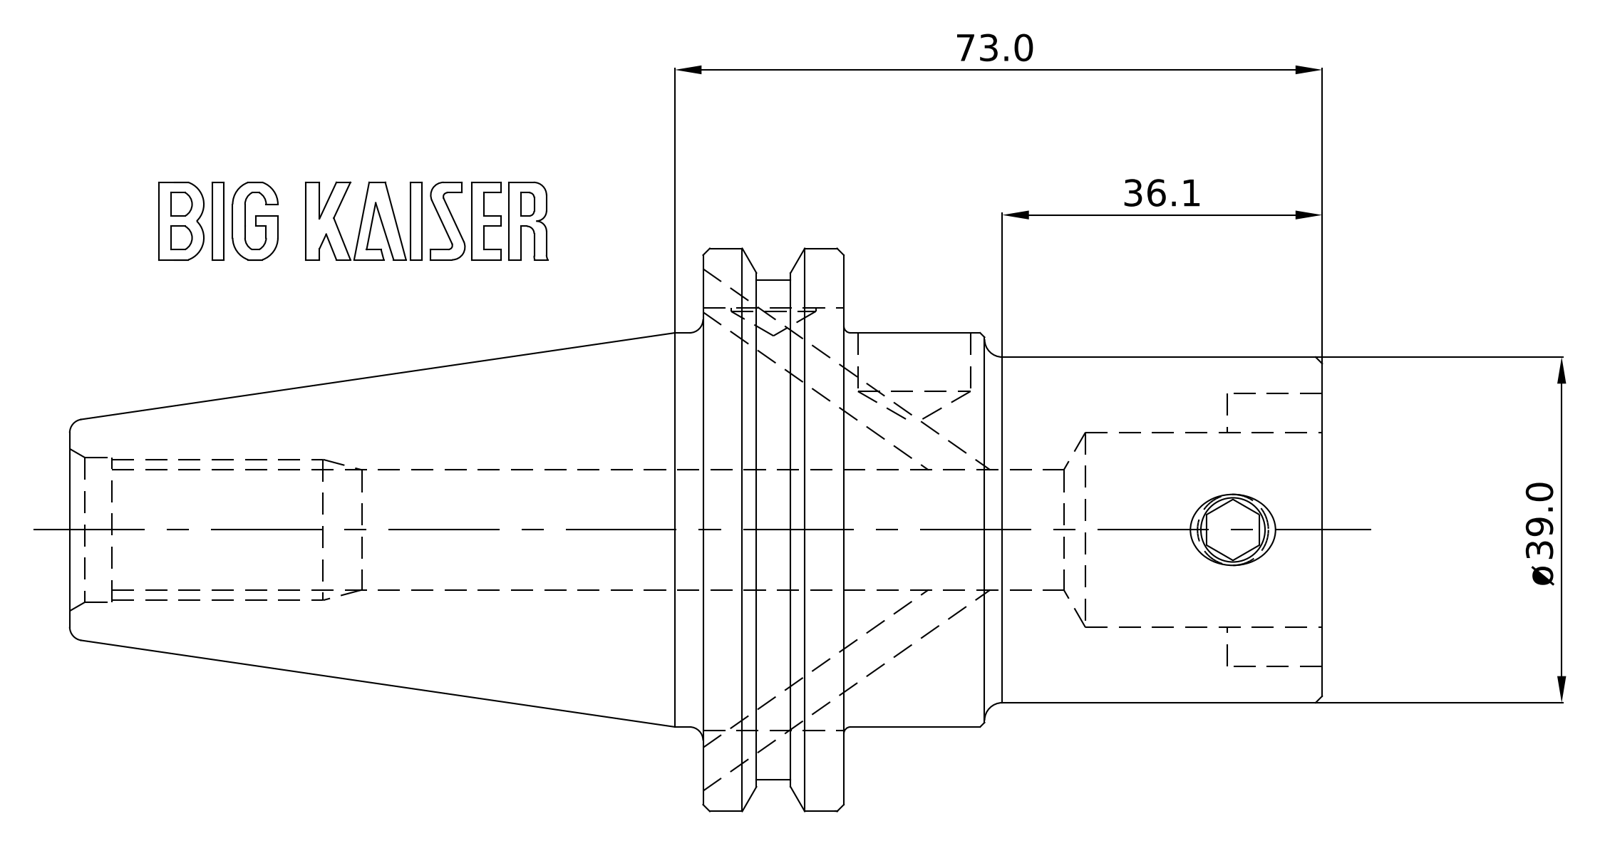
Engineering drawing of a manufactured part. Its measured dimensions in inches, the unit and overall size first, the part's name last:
Units: inches
Overall size (bounding box): 5.561 × 2.5 × 2.5
Round bosses / shafts (diameter × count): ⌀2.5 ×1, ⌀2.219 ×1, ⌀1.75 ×1, ⌀1.535 ×1
Main face-to-face distances: 0.625, 2.124, 2.749, 5.561, 3.437, 2.812, 1.494, 0.63, 1.255, 4.067
Volume: 11.44 in³ · Surface area: 37.21 in²
Bodies: 1 solid, 16 faces (7 planar, 6 cylindrical, 3 other)
Part name (STEP PRODUCT): 11.326.841
STEP written by: SolidWorks 2021 (CONFIG_CONTROL_DESIGN)
